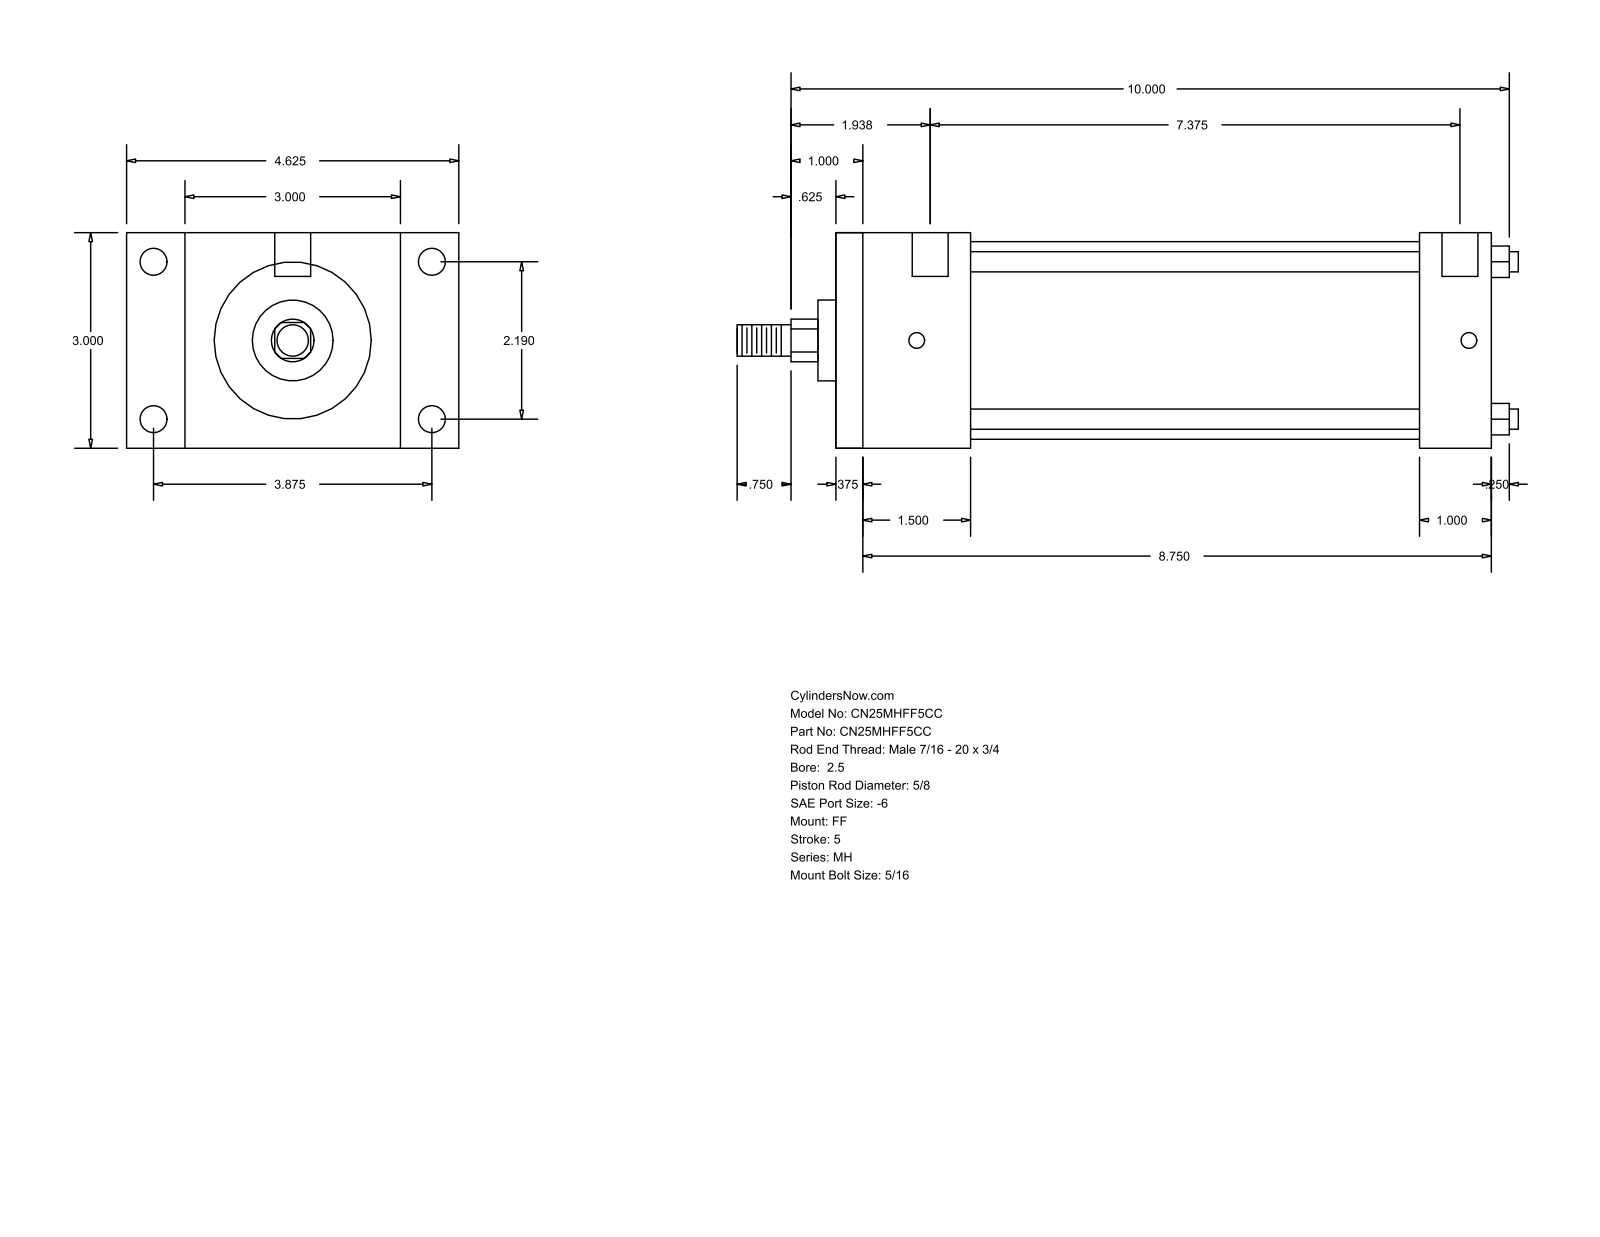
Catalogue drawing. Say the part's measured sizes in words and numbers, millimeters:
The part is named "MH_FF__0250_0.625". Its 3-D file was written by "GSSL Pune (CONFIG_CONTROL_DESIGN)". It is 0 solids with 92 faces: 64 planar, 28 cylindrical and 0 other. Overall it measures 276.23 by 117.47 by 76.2 millimeters. Round holes: 4 of diameter 5.56, 4 of diameter 9.53, 2 of diameter 12.7. Round bosses or shafts: 4 of diameter 7.14, 1 of diameter 69.85, 1 of diameter 28.57, 1 of diameter 15.88, 1 of diameter 11.11. Partial cylindrical surfaces (rounded edges, fillets, slot ends): 1 of radius 7.54. The main face-to-face distances are 76.2, 231.77, 222.25, 9.52, 25.4, 47.62, 206.37, 38.1, 196.85, 158.75. The hole center spacings are 55.62, 98.42, 113.05, 195.26, 3.17, 4.76, 187.33, 190.5.
